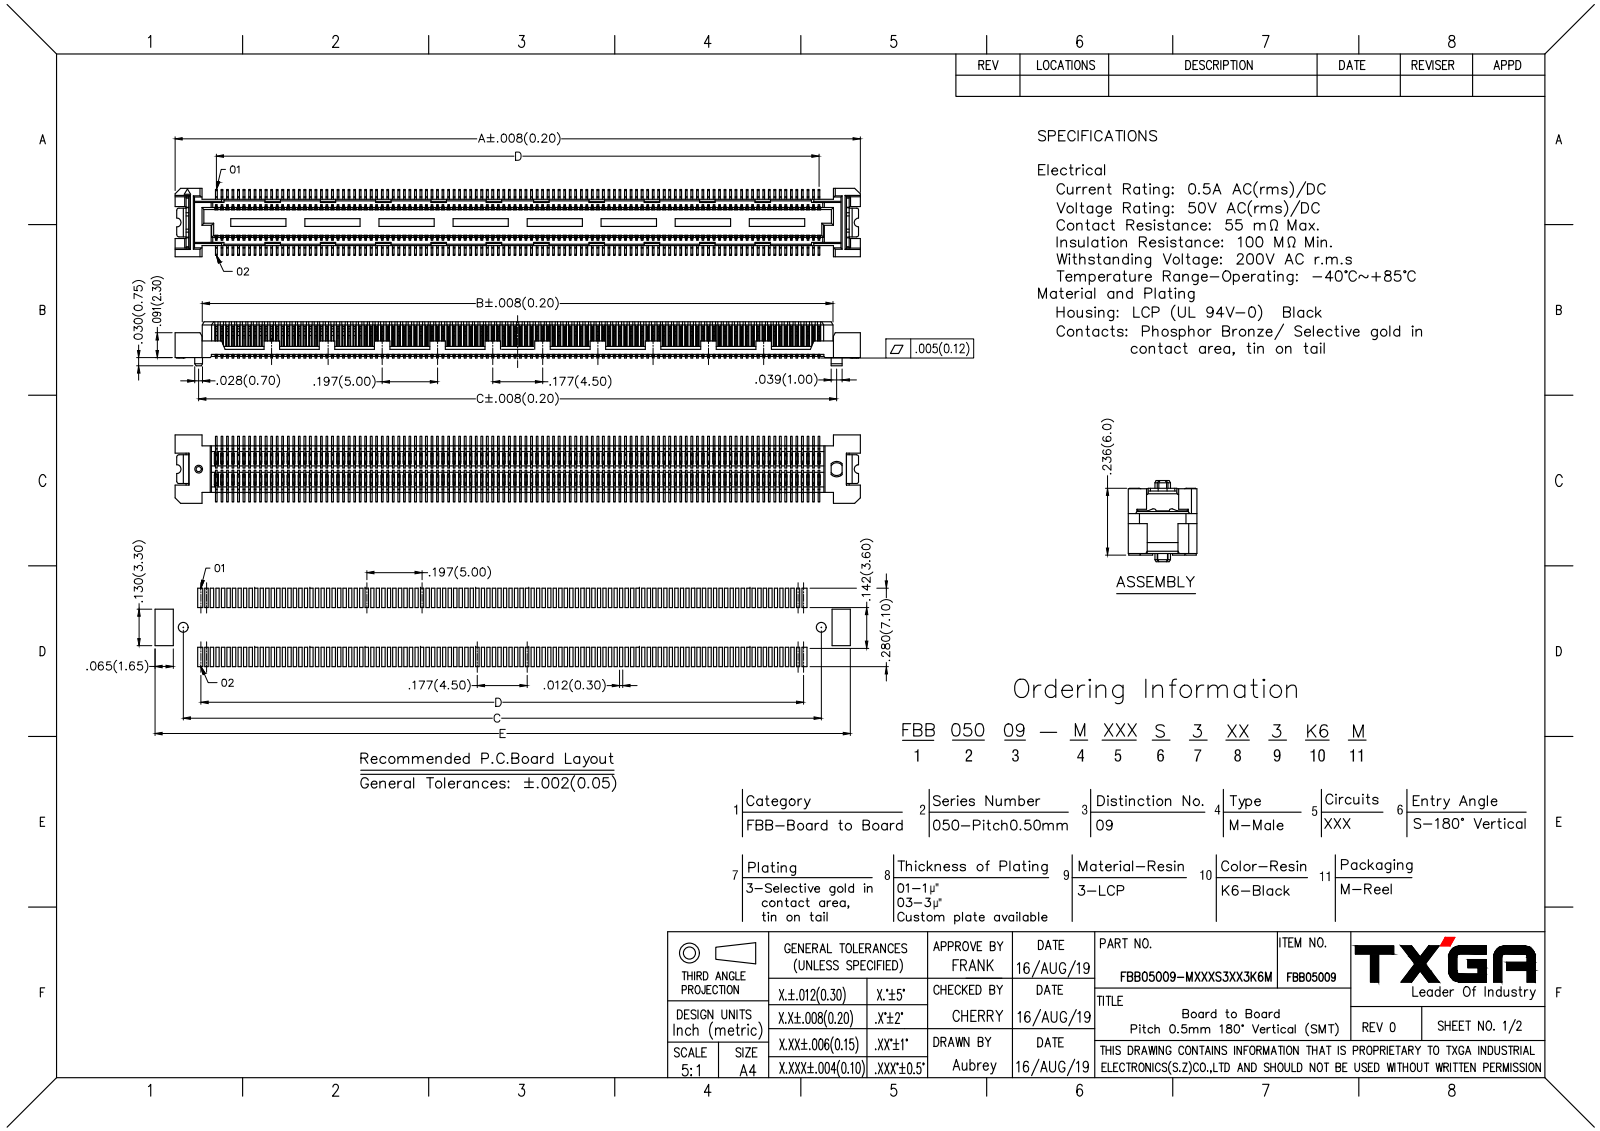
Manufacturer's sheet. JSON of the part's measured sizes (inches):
{"part_name": "JP1", "step_written_by": "PRO/ENGINEER BY PARAMETRIC TECHNOLOGY CORPORATION, 2008380 (CONFIG_CONTROL_DESIGN)", "units": "inches", "bodies": {"solids": 1, "faces": 1986, "planar": 1976, "cylindrical": 4, "other": 6}, "overall_size": [2.439, 0.244, 0.157], "volume_in3": 0.03, "surface_area_in2": 2.694, "round_bosses_or_shafts": [[0.028, 1]], "face_to_face_distances": [0.037, 0.069, 0.106, 0.116, 0.128, 0.029, 0.066, 0.098, 0.135, 0.031]}
